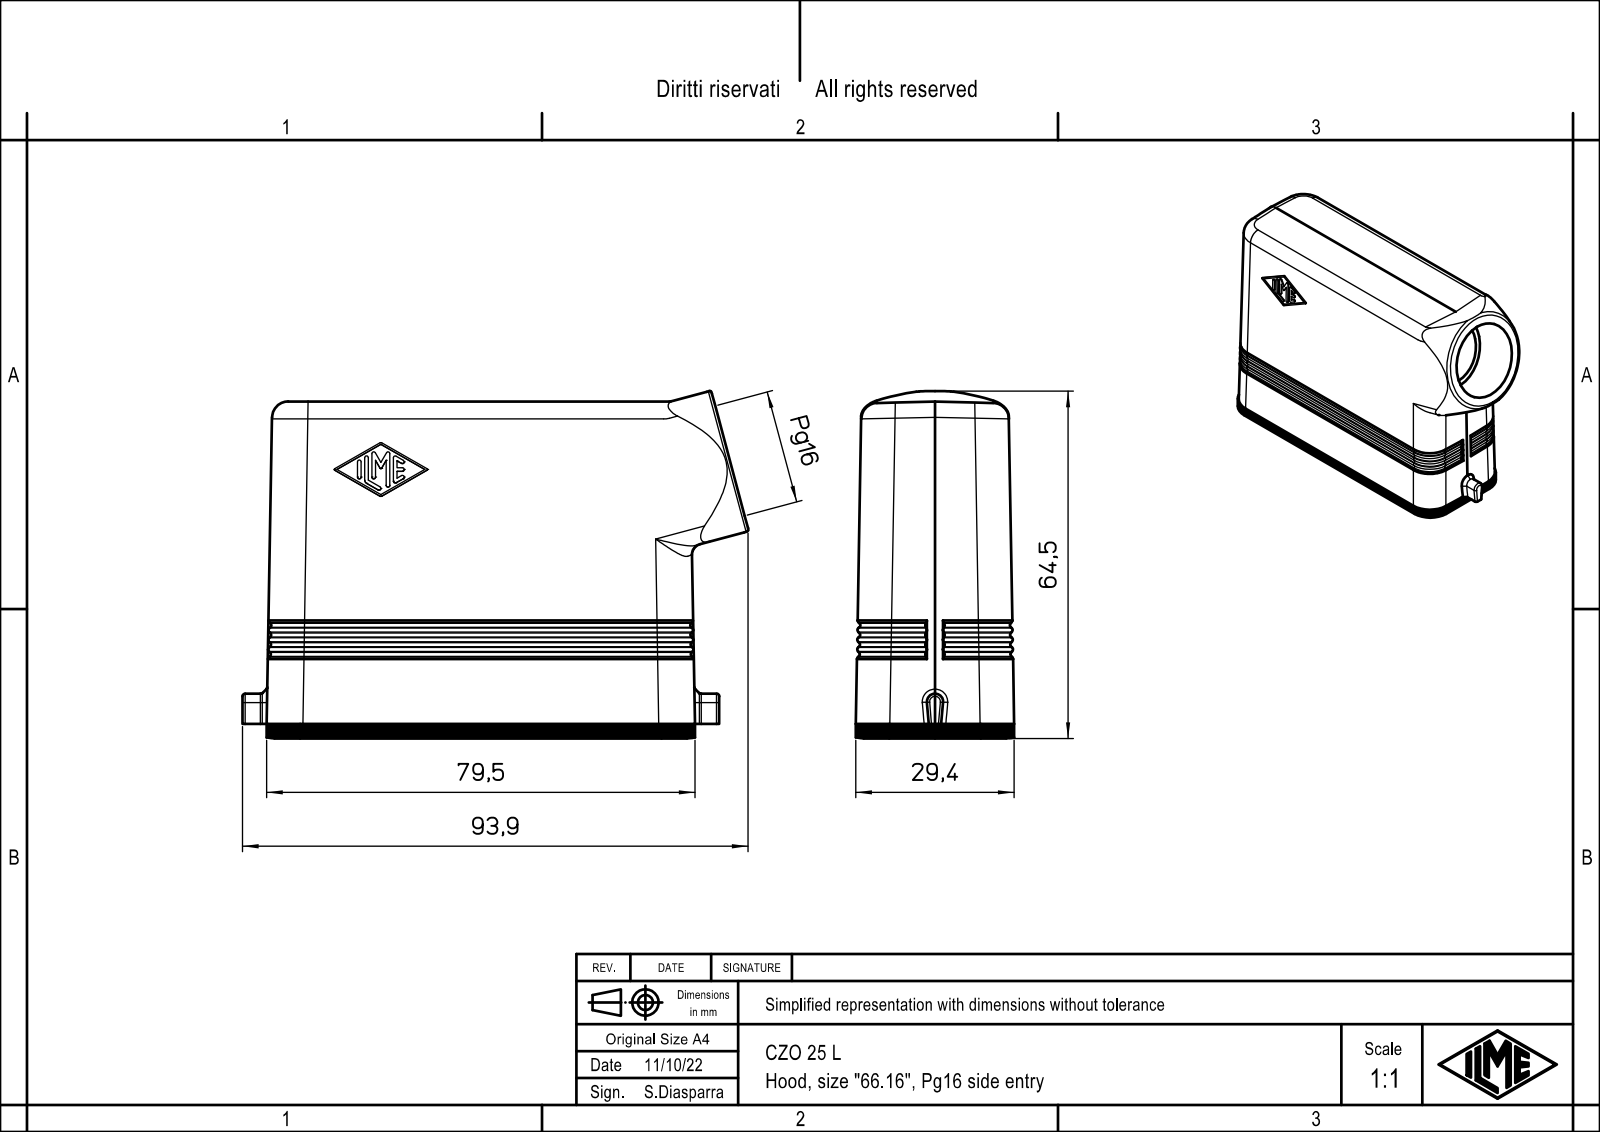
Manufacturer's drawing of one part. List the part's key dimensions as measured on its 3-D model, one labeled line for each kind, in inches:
Part name (STEP PRODUCT): CZO_25_L
STEP written by: PTC Creo Elements/Direct Modeling 19.0B 21-Mar-2015 (C) Parametric Technology GmbH (AUTOMOTIVE_DESIGN)
Units: inches
Bodies: 1 solid, 320 faces (176 planar, 91 cylindrical, 53 other)
Overall size (bounding box): 3.859 × 2.549 × 1.158
Volume: 3.259 in³ · Surface area: 48.95 in²
Round holes (diameter × count): ⌀0.097 ×4, ⌀0.138 ×4, ⌀0.709 ×1, ⌀0.835 ×1
Round bosses / shafts (diameter × count): ⌀0.142 ×1
Partial cylindrical surfaces — rounded edges, fillets, slot ends (radius × count): R0.01 ×14, R0.157 ×8, R0.079 ×7, R0.049 ×4, R0.13 ×4, R0.165 ×2
Main face-to-face distances: 0.118, 1.039, 1.157, 0.921, 2.746, 0.384, 2.628, 0.266, 3.012, 0.044
Hole centre spacings: 0.63, 2.598, 2.674
